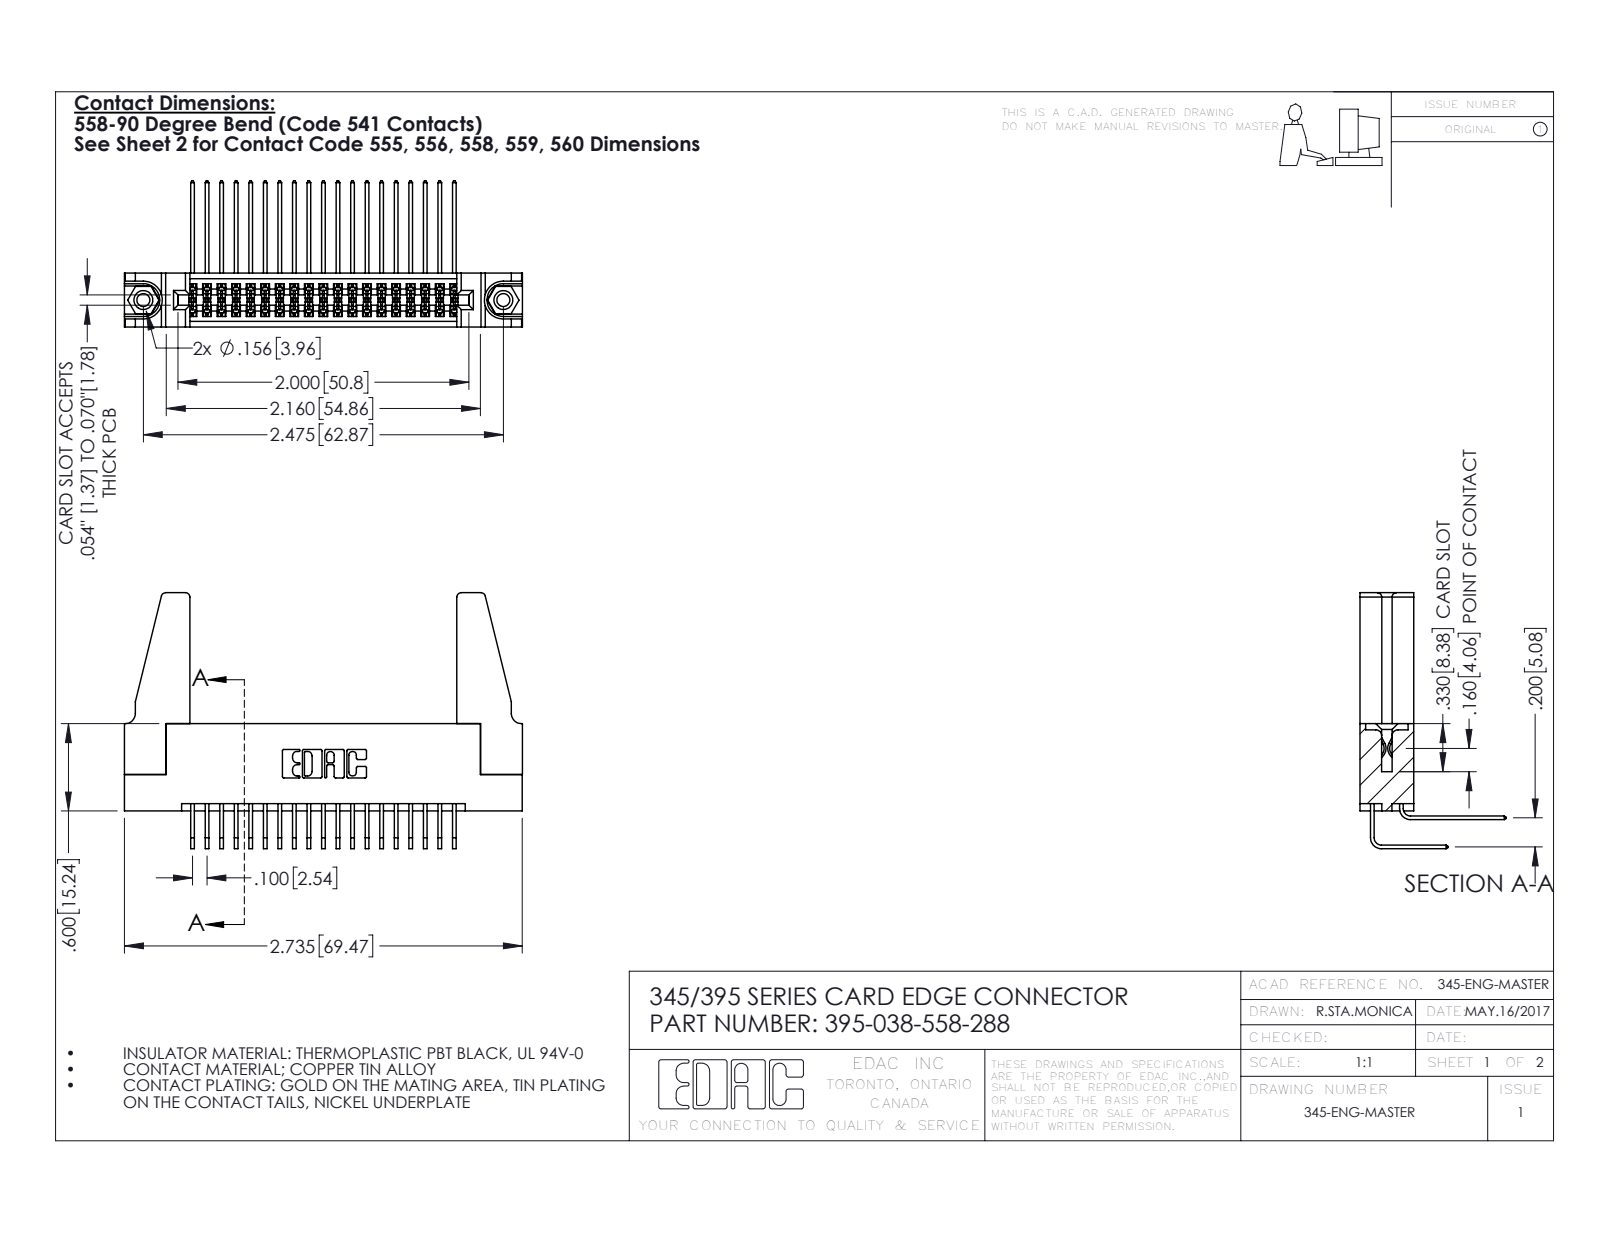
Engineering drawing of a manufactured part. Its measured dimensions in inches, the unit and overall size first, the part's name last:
Units: inches
Overall size (bounding box): 2.736 × 1.759 × 1.005
Round holes (diameter × count): ⌀0.089 ×2, ⌀0.125 ×2, ⌀0.156 ×2, ⌀0.064 ×1
Round bosses / shafts (diameter × count): ⌀0.155 ×2
Partial cylindrical surfaces — rounded edges, fillets, slot ends (radius × count): R0.006 ×58, R0.01 ×22, R0.03 ×8, R0.007 ×6, R0.031 ×6, R0.026 ×3, R0.014 ×2, R0.019 ×2
Main face-to-face distances: 0.072, 0.37, 0.2, 0.298, 0.098, 0.272, 0.025, 0.225, 0.285, 0.309
Hole centre spacings: 0.27, 2.241, 2.475
Volume: 0.611 in³ · Surface area: 21.23 in²
Bodies: 43 solids, 2226 faces (1482 planar, 728 cylindrical, 16 other)
Part name (STEP PRODUCT): 345 Part_Flush Mounting Lugs - 0.156 Dia-TH; 395-038-558-288; 345-292-001_558 559 Tail - 1; 345-292-001_558 Tail - 2 (+2 more)
STEP written by: SolidWorks 2016 (CONFIG_CONTROL_DESIGN)
